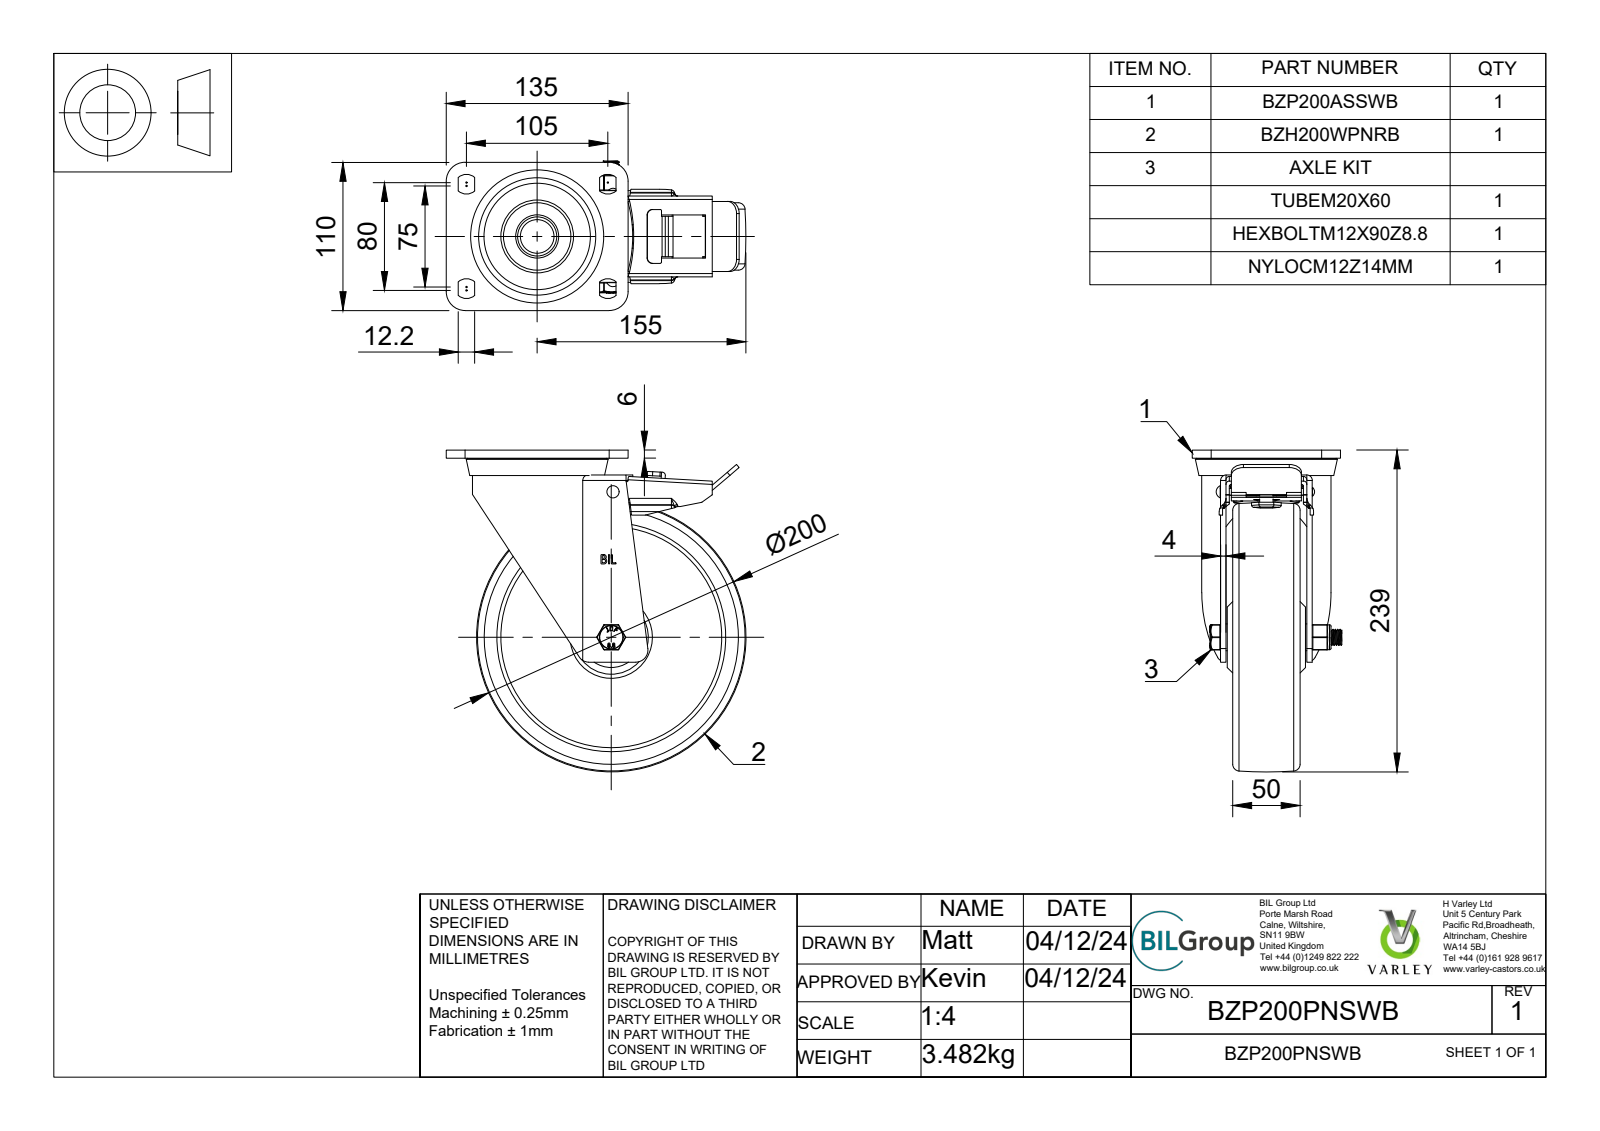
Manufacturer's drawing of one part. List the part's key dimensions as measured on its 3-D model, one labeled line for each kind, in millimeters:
Part name (STEP PRODUCT): BZP200PNSWB v4; BZP200ASSWB v1; ZINC PLATED, PRESSED STEEL TOP PLATE; ZINC PLATED, PRESSED STEEL TOP PLATE Geometry (+8 more)
STEP written by: Autodesk Translation Framework v13.20.0.188 (AP242_MANAGED_MODEL_BASED_3D_ENGINEERING_MIM_LF)
Units: millimetres
Bodies: 27 solids, 903 faces (520 planar, 270 cylindrical, 113 other)
Overall size (bounding box): 239 × 222.5 × 111
Volume: 1 127 000 mm³ · Surface area: 375 607 mm²
Round holes (diameter × count): ⌀30 ×2, ⌀5 ×1, ⌀10 ×1, ⌀12 ×1, ⌀12.2 ×1, ⌀12.5 ×1, ⌀14 ×1, ⌀19 ×1, ⌀20 ×1, ⌀20.5 ×1, ⌀32 ×1, ⌀36 ×1
Round bosses / shafts (diameter × count): ⌀5 ×10, ⌀103.5 ×1, ⌀96 ×1, ⌀83 ×1, ⌀55 ×1, ⌀50 ×1, ⌀29.5 ×1, ⌀29 ×1
Partial cylindrical surfaces — rounded edges, fillets, slot ends (radius × count): R0.5 ×20, R1.5 ×9, R9.09 ×8, R1.25 ×6, R2.5 ×6, R4 ×6, R1 ×5, R2 ×5
Main face-to-face distances: 4, 55, 9, 11, 5, 24.5, 59, 26.5, 35.5, 6
Hole centre spacings: 108.03
